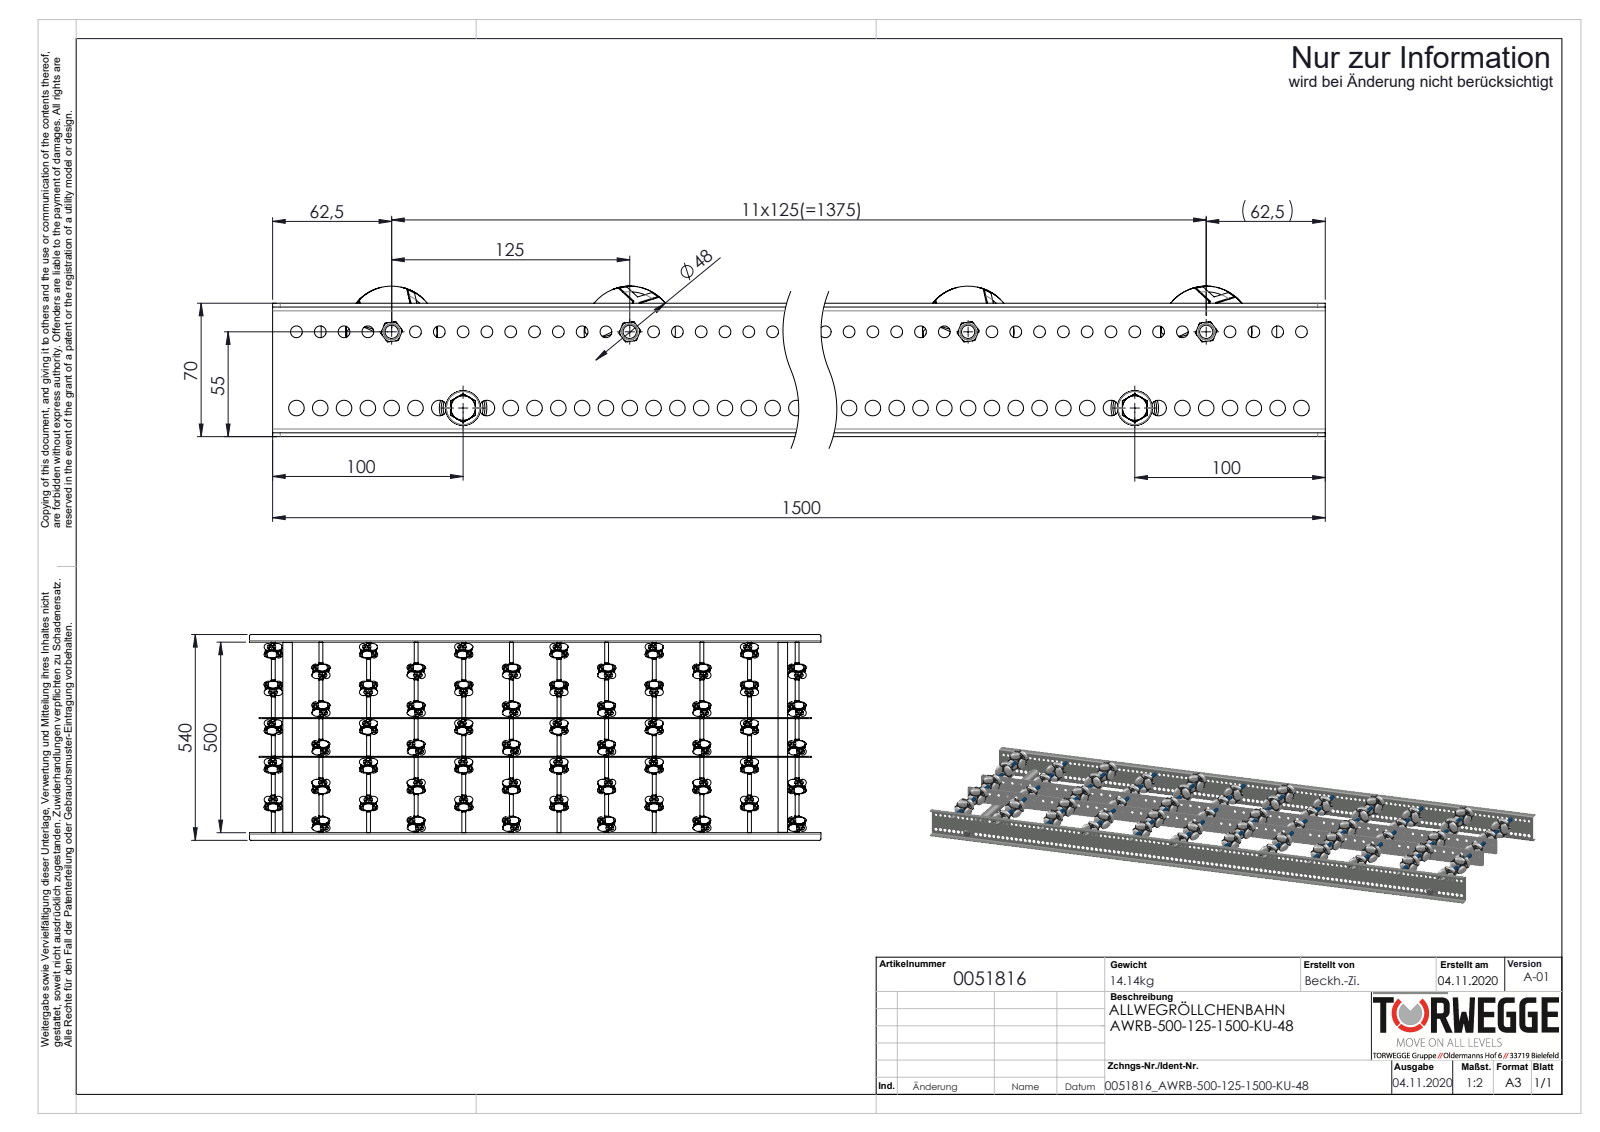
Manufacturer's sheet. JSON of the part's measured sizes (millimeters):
{"part_name": "S100994_Sperrzahnschraube_M08x16-8.8-A2K; 0051816; Traversen_KFG_L500; AWR-Achse-für-Konfiguration_L500 (+8 more)", "step_written_by": "SolidWorks 2020 (AUTOMOTIVE_DESIGN)", "units": "millimeters", "bodies": {"solids": 1010, "faces": 18596, "planar": 6228, "cylindrical": 7608, "other": 4760}, "overall_size": [1500, 540, 79], "volume_mm3": 3928000, "surface_area_mm2": 2842000, "round_holes": [[3.7, 360], [4.2, 360], [6.2, 119], [8.2, 119], [6.5, 58], [4.92, 12], [8.4, 12], [6.8, 2], [21, 2]], "round_bosses_or_shafts": [[4, 360], [3.7, 315], [8, 14], [42, 12], [11, 12], [10, 12], [7, 12], [6, 12]], "partial_cylinders_radius": [[23.55, 12], [4, 8], [2, 4], [5, 4]], "face_to_face_distances": [2, 502, 101.5, 2.5, 68, 500, 504, 99, 200.1, 301.6], "hole_center_spacings": [36.05, 36.06, 36.07, 36.04, 7.75, 10, 15.5, 55.27]}
